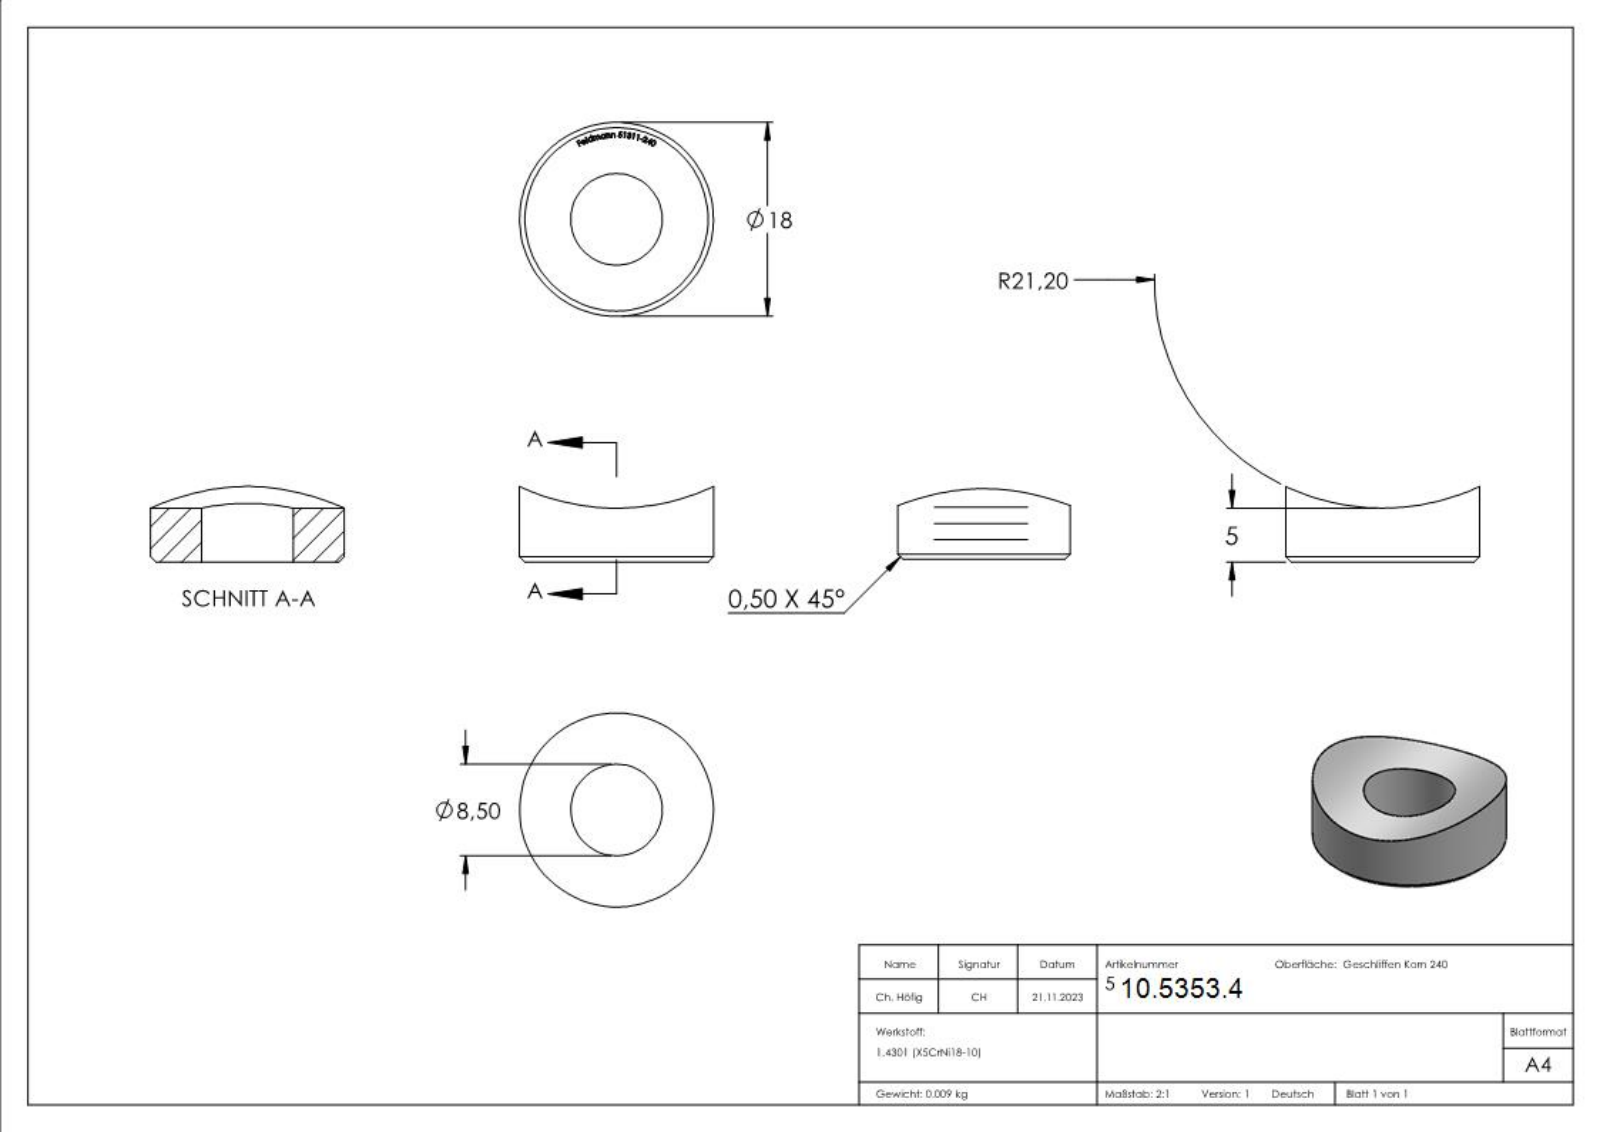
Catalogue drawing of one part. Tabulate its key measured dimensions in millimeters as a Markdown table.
| quantity | value |
| --- | --- |
| part name | 51311-240 |
| STEP written by | SolidWorks 2018 (CONFIG_CONTROL_DESIGN) |
| units | millimeters |
| bodies | 1 solid, 216 faces (127 planar, 3 cylindrical, 86 other) |
| overall size | 18 × 18 × 7 |
| volume | 1 100 mm³ |
| surface area | 866 mm² |
| round holes (diameter × count) | 8.5 × 1 |
| round bosses / shafts (diameter × count) | 18 × 1 |
| partial cylindrical surfaces (radius × count) | 21.2 × 1 |
| main face-to-face distances | 0.53, 0.58, 0.32, 0.48, 0.31, 0.39, 0.52, 0.54, 0.47, 0.38 |
